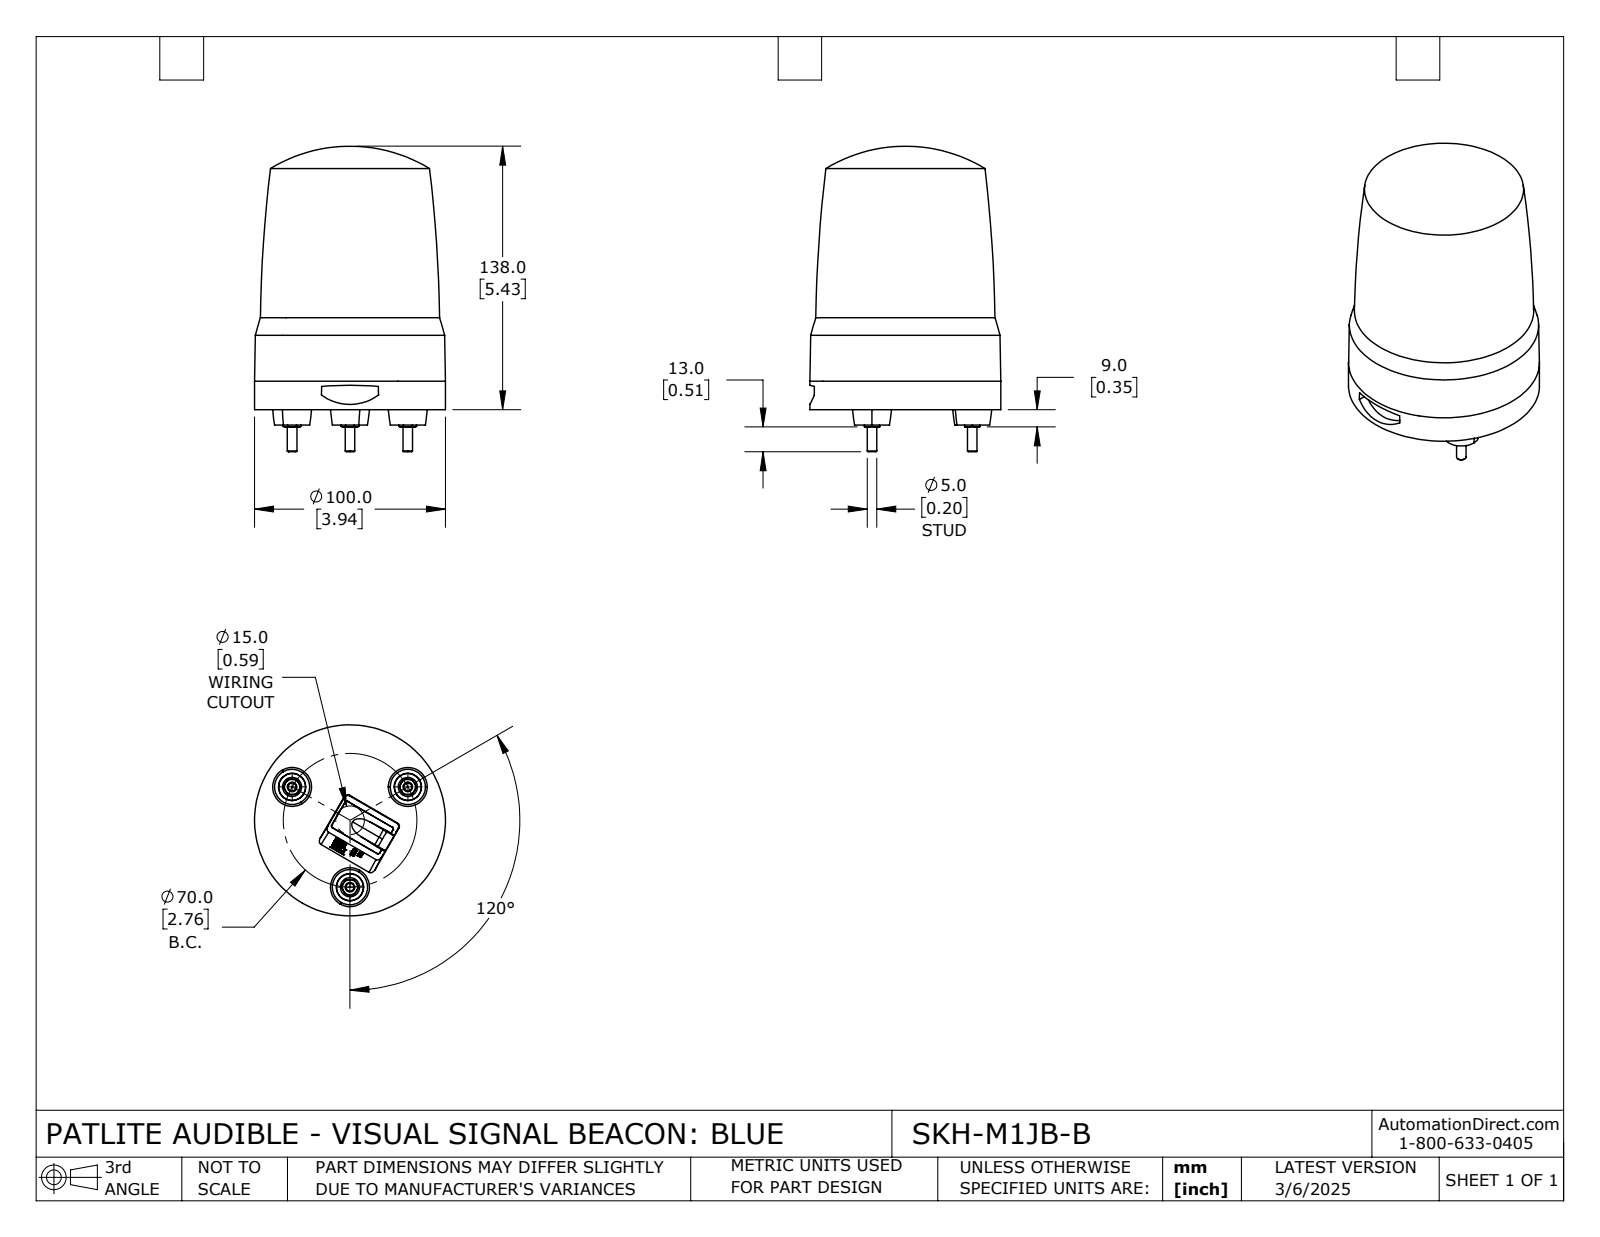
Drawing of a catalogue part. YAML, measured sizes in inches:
part_name: "SKH-M1JB-B"
step_written_by: "SolidWorks 2024 (CONFIG_CONTROL_DESIGN)"
units: inches
bodies: {solids: 1, faces: 446, planar: 211, cylindrical: 22, other: 213}
overall_size: [6.299, 3.937, 3.937]
volume: 54.94
surface_area: 85.92
round_bosses_or_shafts:
  - {diameter: 0.394, count: 3}
  - {diameter: 0.197, count: 3}
  - {diameter: 3.937, count: 1}
partial_cylinders:
  - {radius: 0.079, count: 4}
  - {radius: 0.199, count: 2}
  - {radius: 1.772, count: 1}
  - {radius: 3.154, count: 1}
face_to_face_distances: [0.315, 0.585, 0.27, 0.063, 0.648, 0.333, 0.15, 0.165, 0.435, 0.498]
